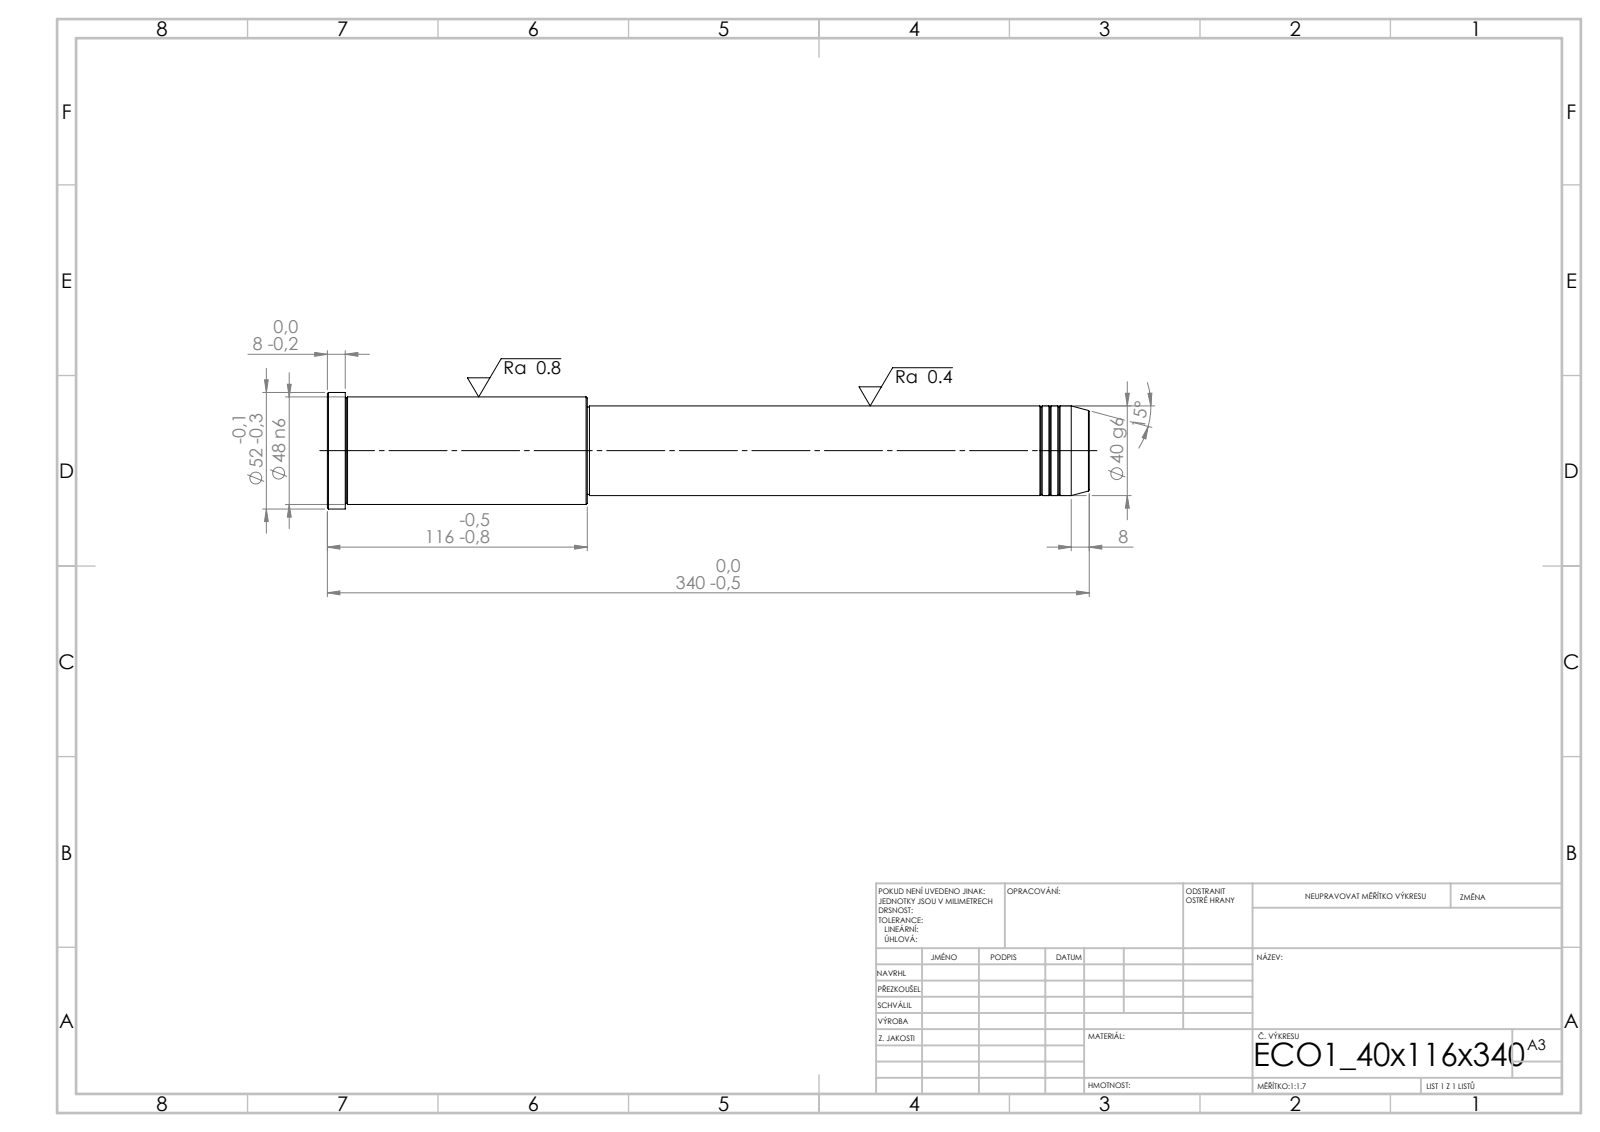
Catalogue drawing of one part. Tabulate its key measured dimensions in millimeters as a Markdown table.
| quantity | value |
| --- | --- |
| STEP written by | SolidWorks 2019 (CONFIG_CONTROL_DESIGN) |
| units | millimeters |
| bodies | 1 solid, 43 faces (5 planar, 14 cylindrical, 24 other) |
| overall size | 340 × 52 × 52 |
| volume | 492 560 mm³ |
| surface area | 50 018 mm² |
| round bosses / shafts (diameter × count) | 52 × 1, 48 × 1, 40 × 1, 39 × 1 |
| main face-to-face distances | 340, 224, 116, 332, 108, 8, 223, 1, 109, 117 |
